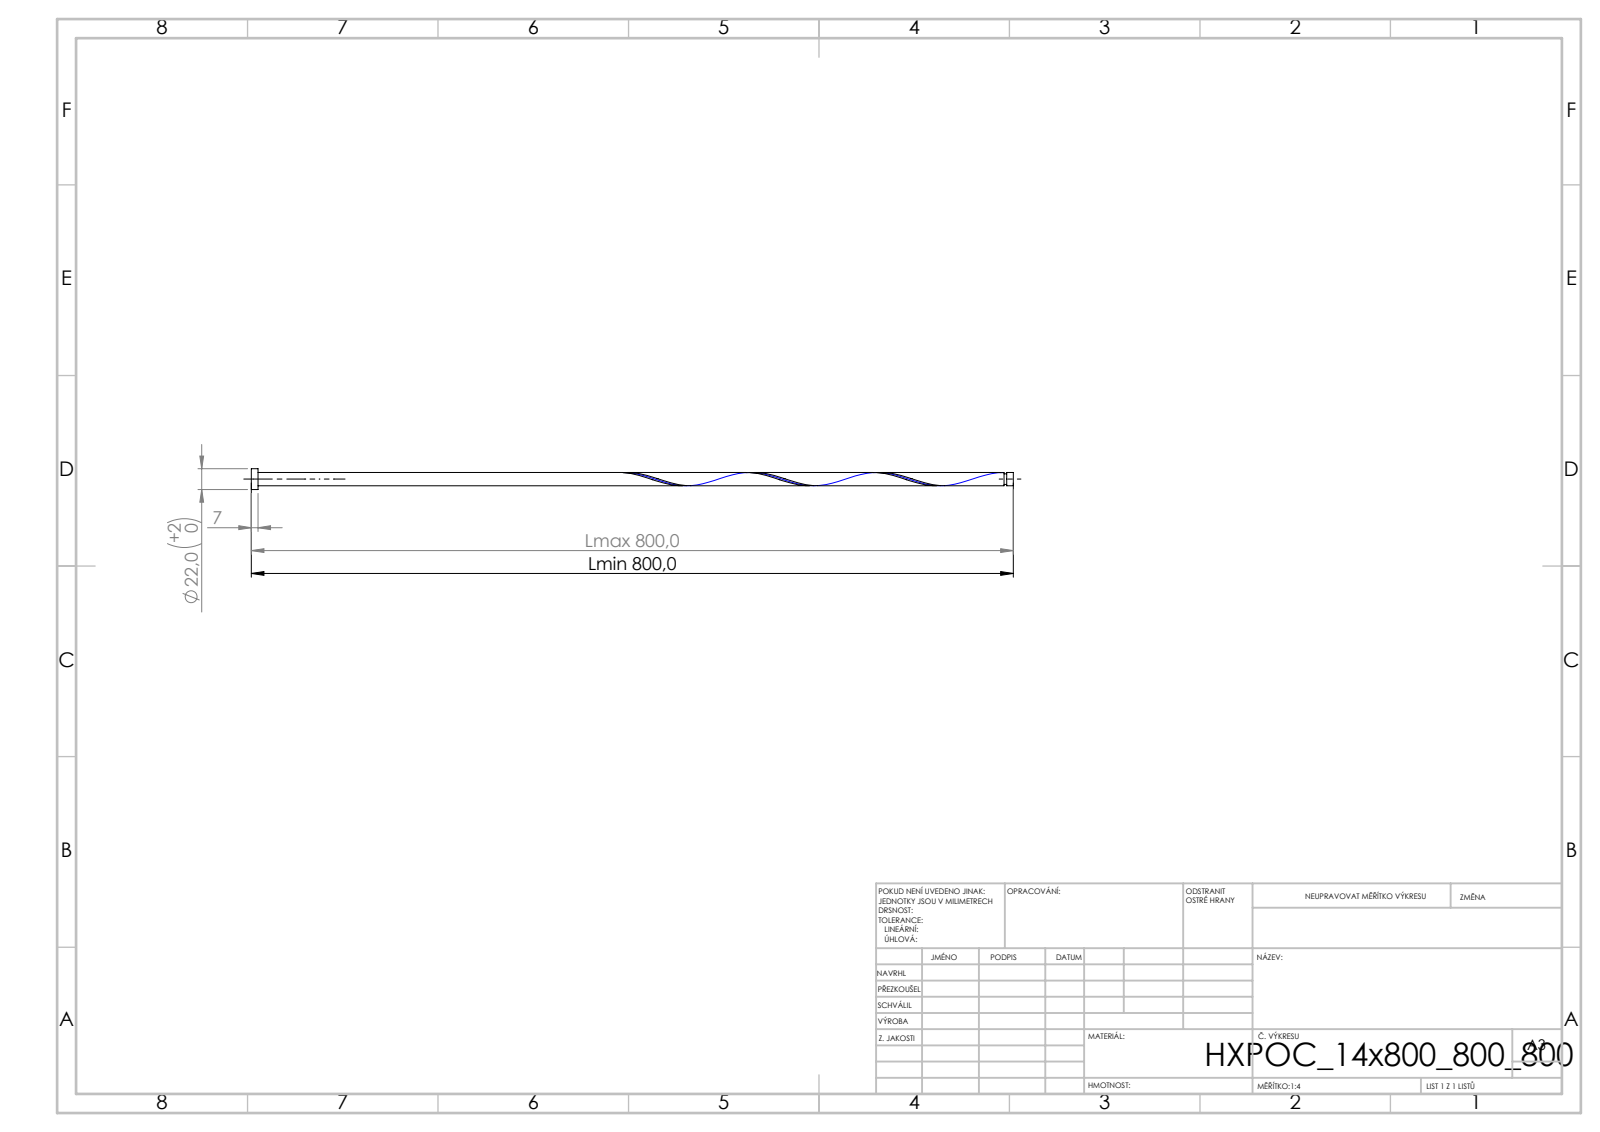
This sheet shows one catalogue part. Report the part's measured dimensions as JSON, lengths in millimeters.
{"step_written_by": "SolidWorks 2019 (CONFIG_CONTROL_DESIGN)", "units": "millimeters", "bodies": {"solids": 1, "faces": 16, "planar": 6, "cylindrical": 9, "other": 1}, "overall_size": [800, 22, 22], "volume_mm3": 150759, "surface_area_mm2": 48500, "round_bosses_or_shafts": [[22, 1], [14, 1], [11.2, 1]], "face_to_face_distances": [7, 800, 793, 793.15, 786.15, 6.85, 790.35, 783.35, 2.8, 9.65]}
